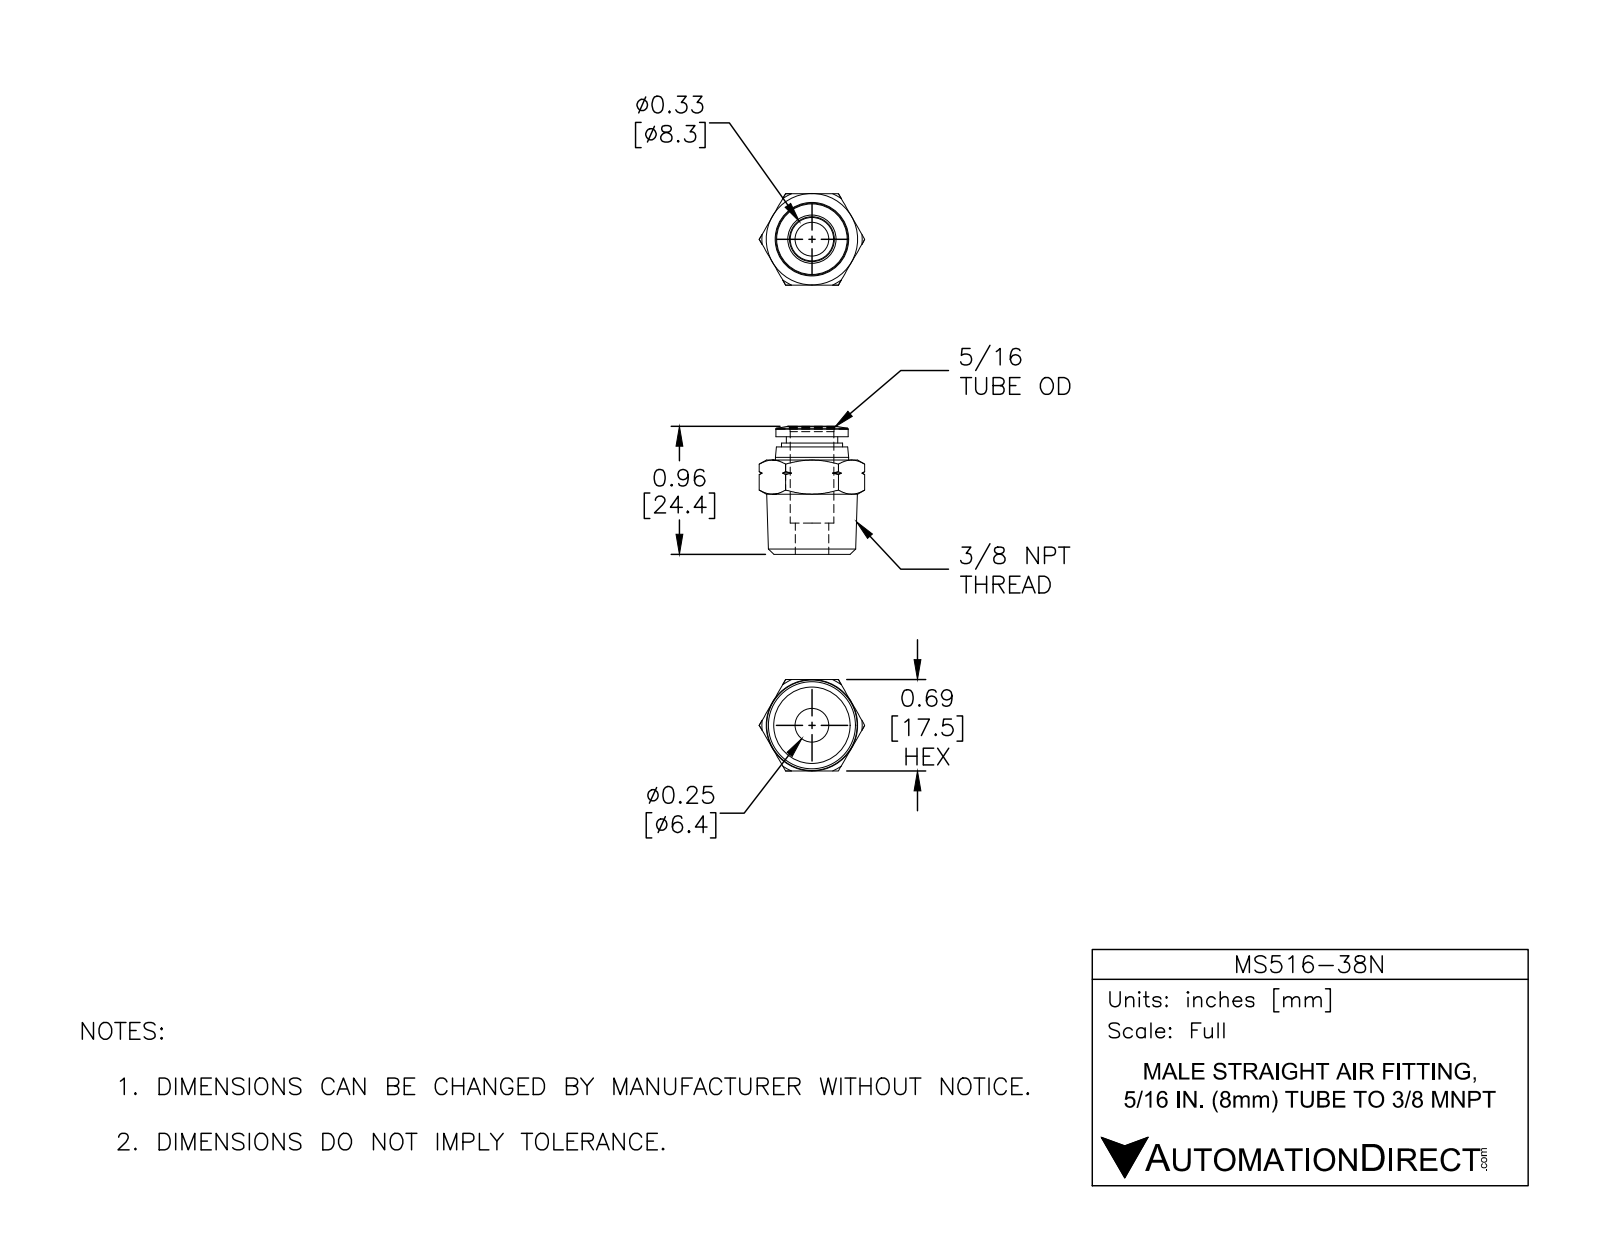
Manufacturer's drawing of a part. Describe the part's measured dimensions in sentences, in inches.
The part is named "MS516-38N". Its 3-D file was written by "SolidWorks 2015 (CONFIG_CONTROL_DESIGN)". It is 1 solid with 63 faces: 13 planar, 12 cylindrical and 38 other. Overall it measures 0.963 by 0.794 by 0.687 inches. Its volume is 0.238 cubic inches and its surface area 3.681 square inches. Round holes: 1 of diameter 0.252, 1 of diameter 0.327. Round bosses or shafts: 1 of diameter 0.551, 1 of diameter 0.543, 1 of diameter 0.461, 1 of diameter 0.386. The main face-to-face distances are 0.687, 0.709, 0.884, 0.175, 0.807, 0.098, 0.077, 0.837, 0.128, 0.03.
